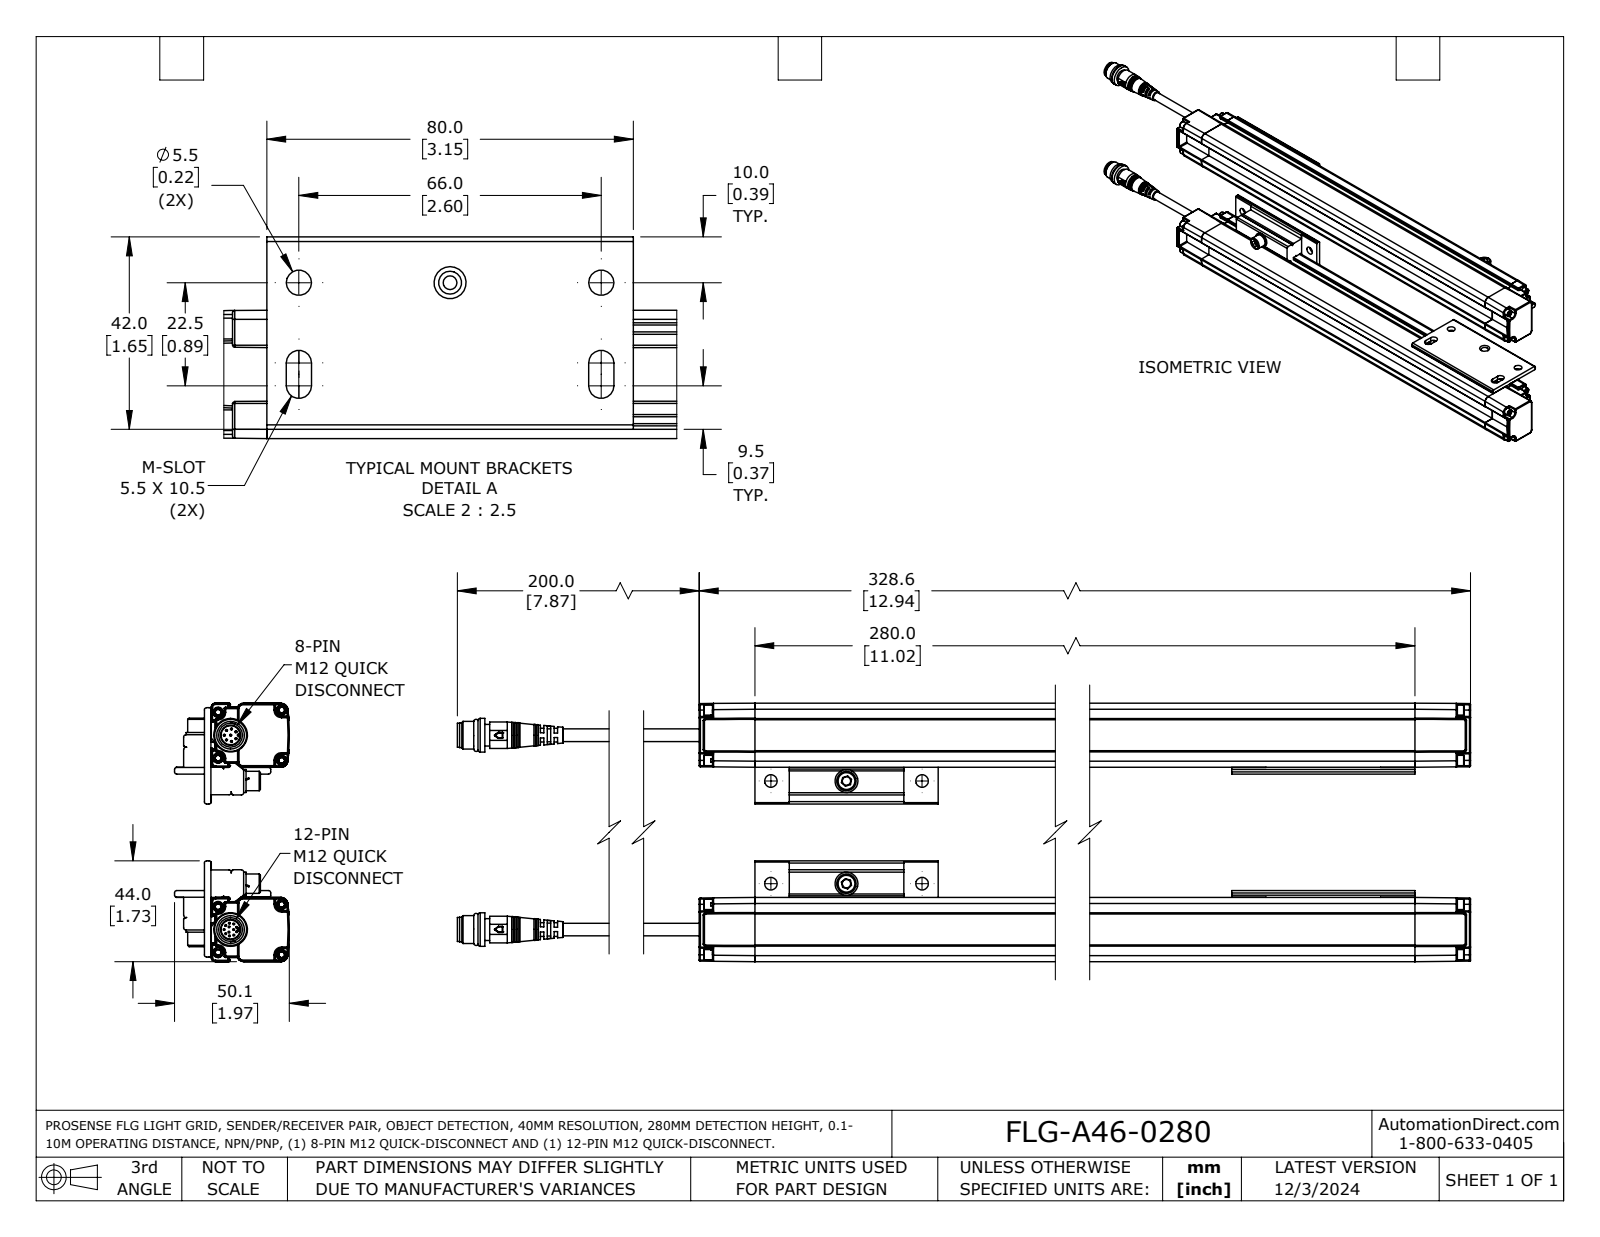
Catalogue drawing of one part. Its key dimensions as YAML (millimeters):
part_name: "FLG-A46-0280"
step_written_by: "SolidWorks 2023 (AUTOMOTIVE_DESIGN)"
units: millimeters
bodies: {solids: 10, faces: 1668, planar: 816, cylindrical: 456, other: 396}
overall_size: [420.55, 112.8, 50.09]
volume: 582176
surface_area: 173558
round_holes:
  - {diameter: 0.4, count: 16}
  - {diameter: 5.5, count: 6}
  - {diameter: 2.5, count: 4}
  - {diameter: 5, count: 3}
  - {diameter: 8.3, count: 2}
round_bosses_or_shafts:
  - {diameter: 0.8, count: 20}
  - {diameter: 4.5, count: 8}
  - {diameter: 3, count: 8}
  - {diameter: 5.5, count: 4}
  - {diameter: 1.5, count: 4}
  - {diameter: 10, count: 3}
  - {diameter: 8.5, count: 3}
  - {diameter: 3.7, count: 3}
partial_cylinders:
  - {radius: 0.5, count: 142}
  - {radius: 1, count: 40}
  - {radius: 0.25, count: 20}
  - {radius: 0.2, count: 12}
  - {radius: 0.3, count: 12}
  - {radius: 2.75, count: 12}
  - {radius: 2.55, count: 6}
  - {radius: 1.25, count: 4}
face_to_face_distances: [84.8, 28, 3, 1.8, 4.8, 7.25, 20.75, 26.45, 56.8, 24.65]
hole_center_spacings: [2.75, 33, 4.15, 24.87, 55.64, 5.45, 44.8, 66]
